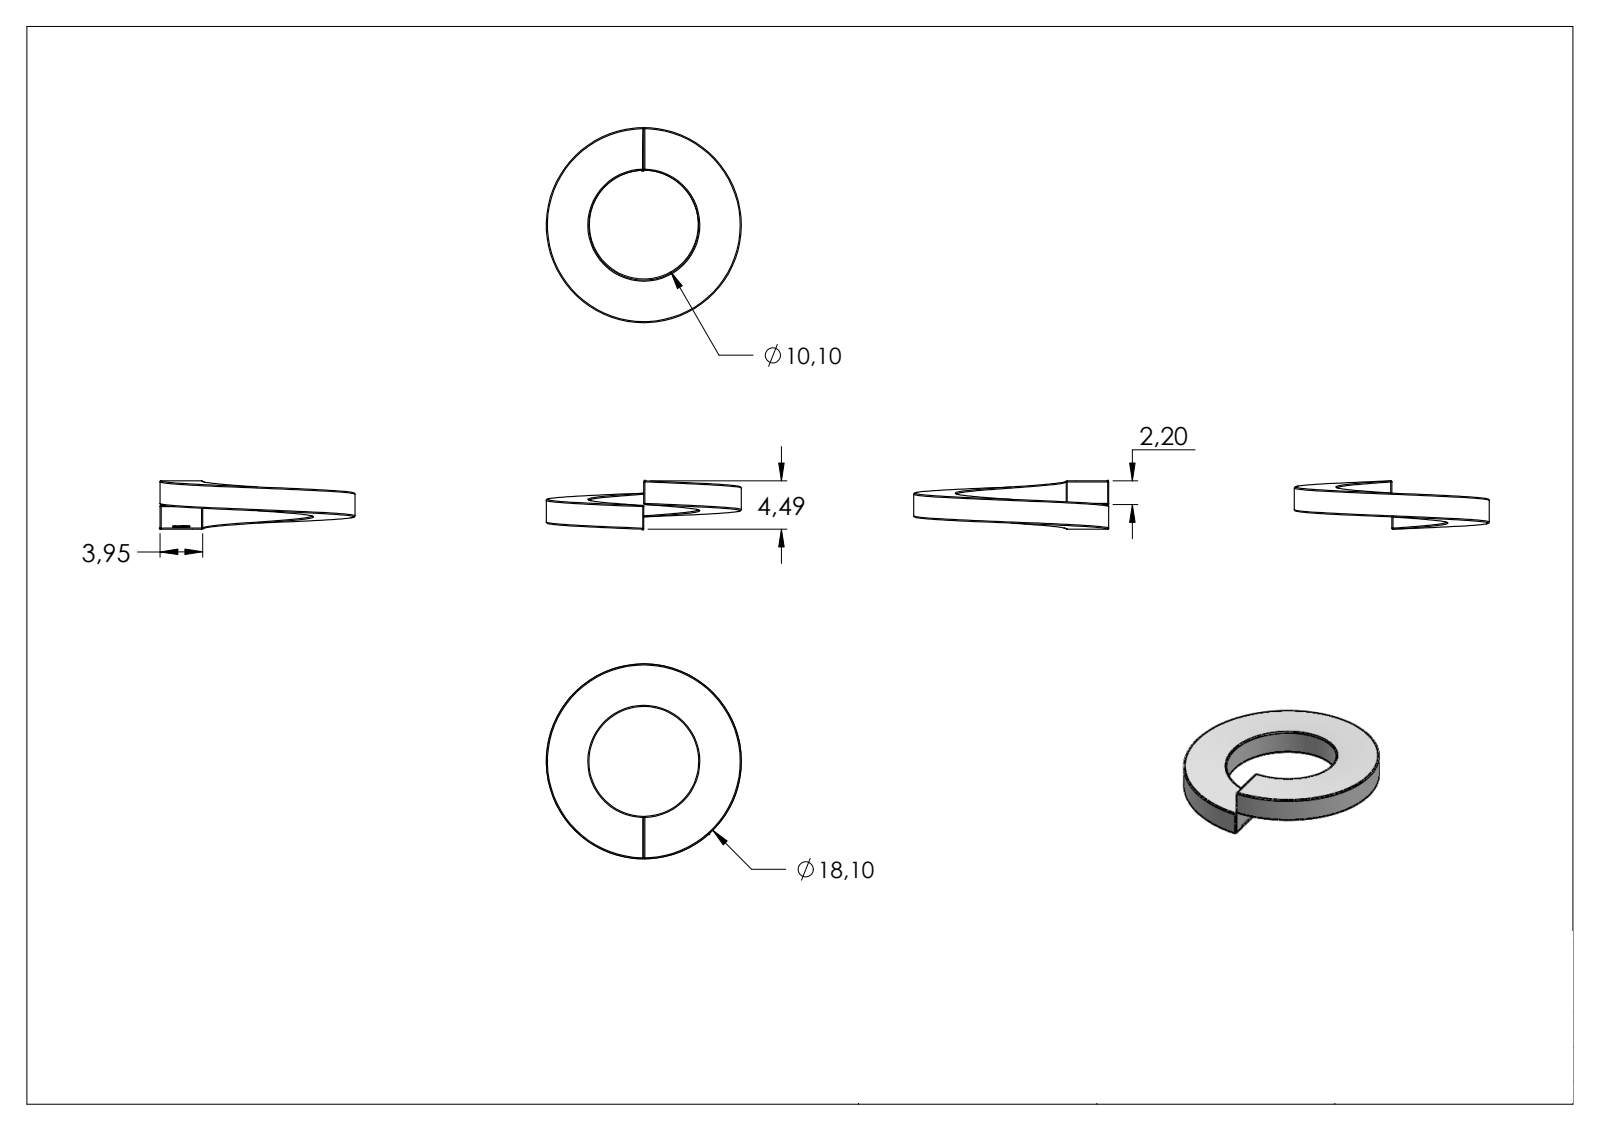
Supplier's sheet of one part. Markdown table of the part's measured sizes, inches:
| quantity | value |
| --- | --- |
| part name | 58319-240-10 |
| STEP written by | SolidWorks 2015 (CONFIG_CONTROL_DESIGN) |
| units | inches |
| bodies | 1 solid, 282 faces (136 planar, 0 cylindrical, 146 other) |
| overall size | 0.713 × 0.713 × 0.177 |
| volume | 0.024 in³ |
| surface area | 0.863 in² |
| main face-to-face distances | 0.019, 0.038, 0.019, 0.039, 0.051, 0.032, 0.02, 0.057, 0.013, 0.044 |
